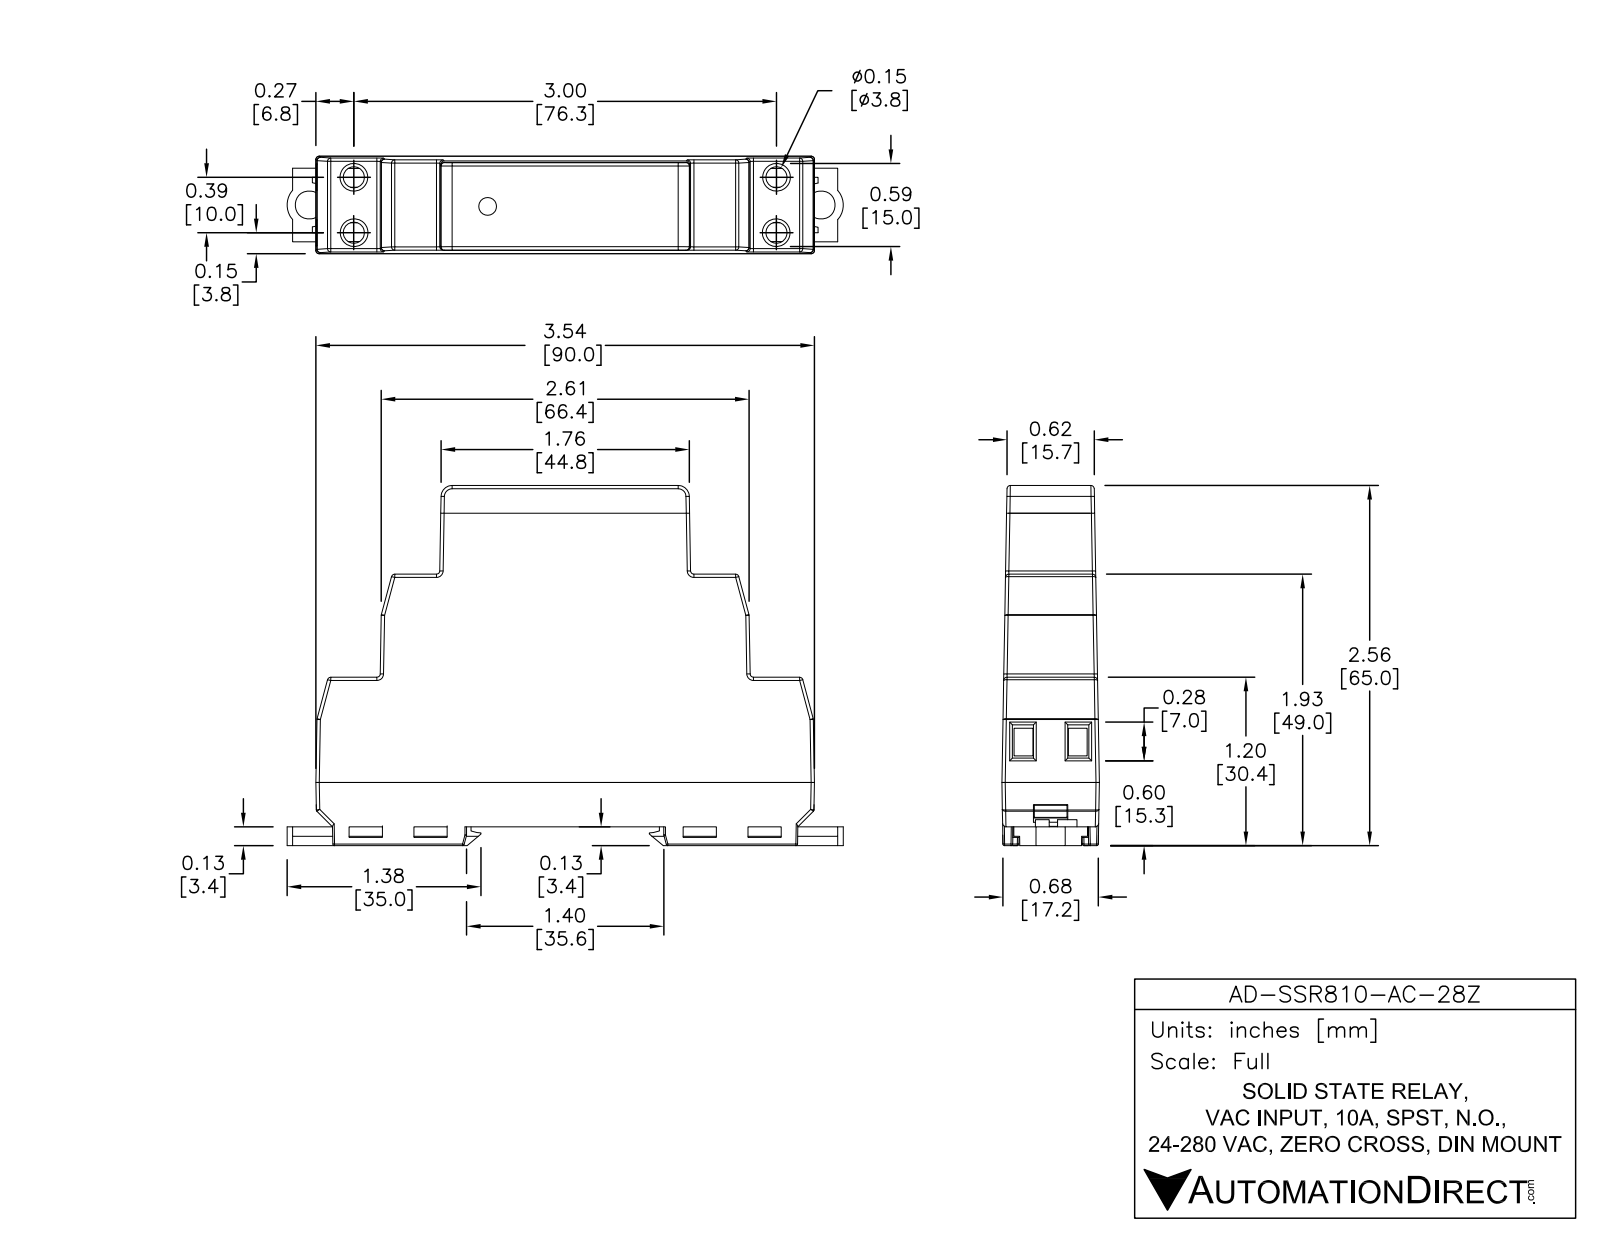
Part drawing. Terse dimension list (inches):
name: AD-SSR810-AC-28Z
written by: SolidWorks 2013 (AUTOMOTIVE_DESIGN)
unit: in
bodies: 1 solid, 835 faces (494 planar, 78 cylindrical, 263 other)
size: 3.924 × 2.616 × 0.685
volume: 4.605 in³; area: 24.23 in²
holes: 4× ⌀0.19, 2× ⌀0.2
bosses: 1× ⌀0.105
rounds: 41× R0.015, 2× R0.06, 2× R0.172
face distances: 2.525, 0.049, 2.574, 0.425, 2.215, 0.025, 0.05, 1.934, 1.885, 0.64
hole spacings: 0.338, 3.3, 0.364, 3.01, 3.032, 3.58
